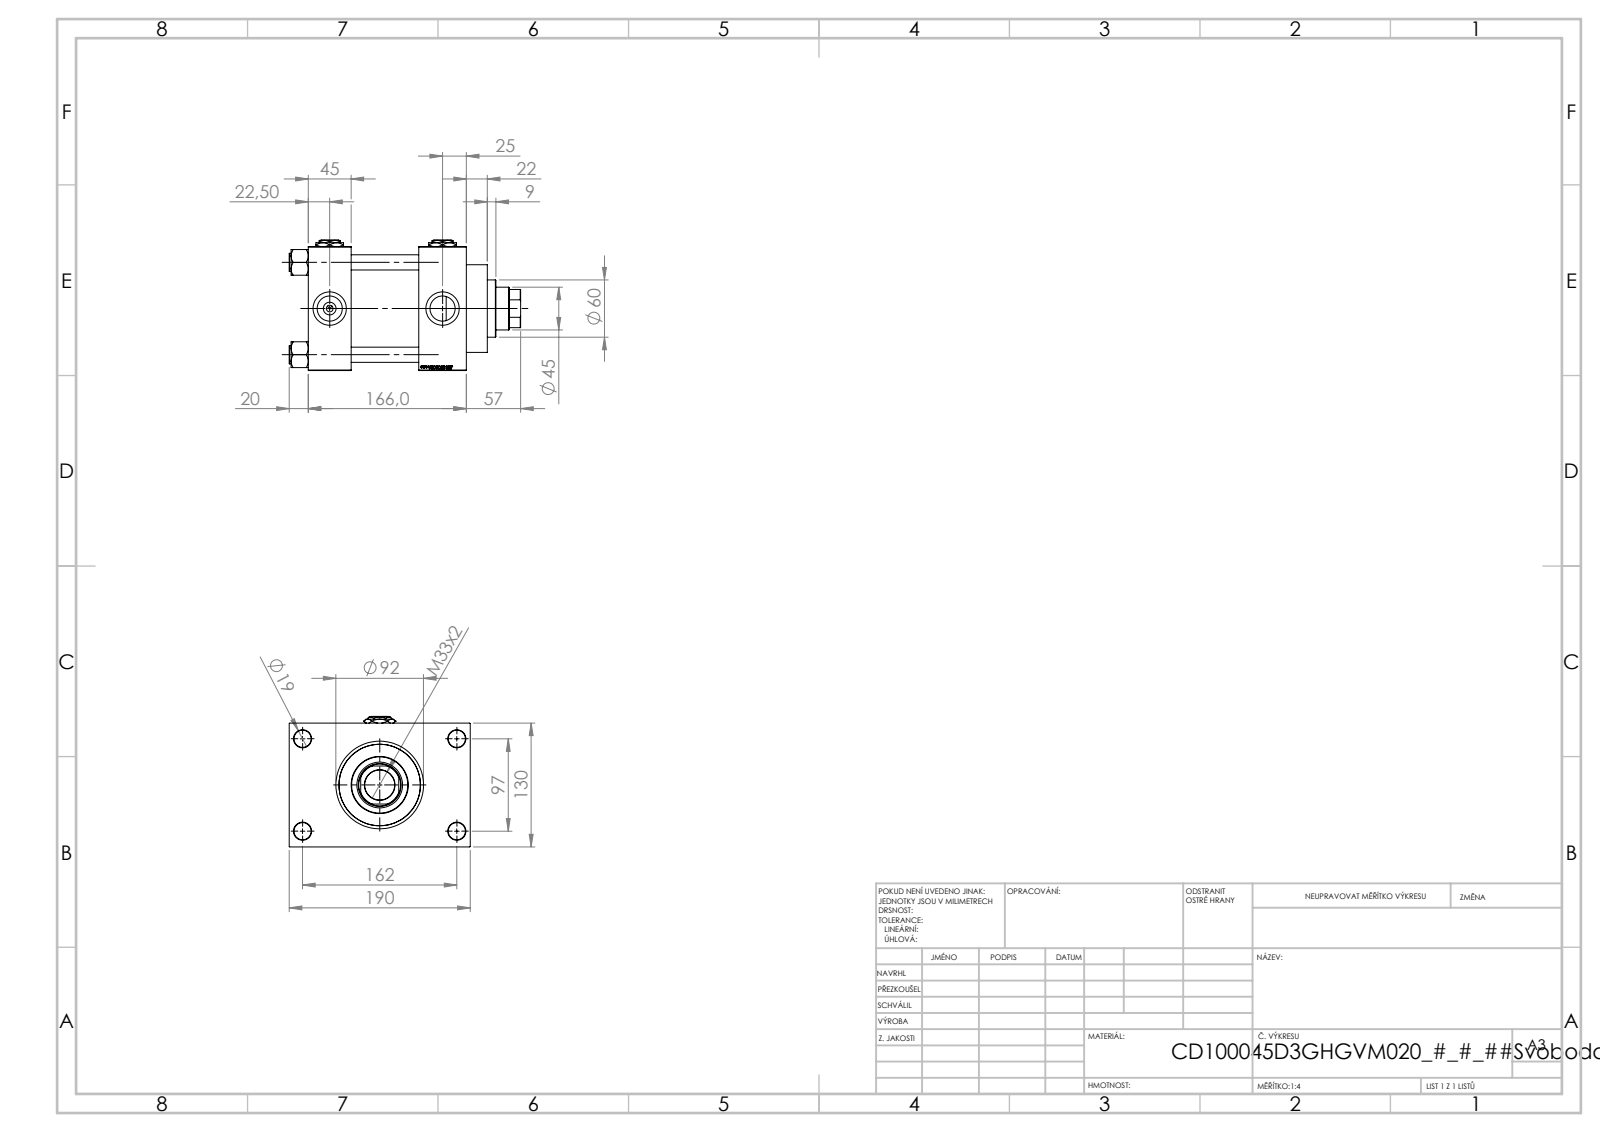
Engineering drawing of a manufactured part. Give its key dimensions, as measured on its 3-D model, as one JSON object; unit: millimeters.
{"part_name": "V215CD_D_TYCINKA; Zatka_pro_OIL_PORT; V215CD_D_Body; V215CD_NUT_M5_D (+2 more)", "step_written_by": "SolidWorks 2019 (CONFIG_CONTROL_DESIGN)", "units": "millimeters", "bodies": {"solids": 13, "faces": 1252, "planar": 593, "cylindrical": 99, "other": 560}, "overall_size": [243, 190, 137], "volume_mm3": 2576000, "surface_area_mm2": 361795, "round_holes": [[16, 4], [18, 4], [26.44, 4], [35, 4], [7, 3], [31.5, 1], [45, 1], [48, 1], [76, 1], [85.5, 1], [100, 1]], "round_bosses_or_shafts": [[19, 4], [106, 1], [92, 1], [60, 1]], "partial_cylinders_radius": [[22, 1]], "face_to_face_distances": [45, 130, 116, 71, 166, 121, 50, 30, 160, 20], "hole_center_spacings": [32.55, 68.52, 94.41, 96.9, 102.27, 129.45, 161.73, 97]}
